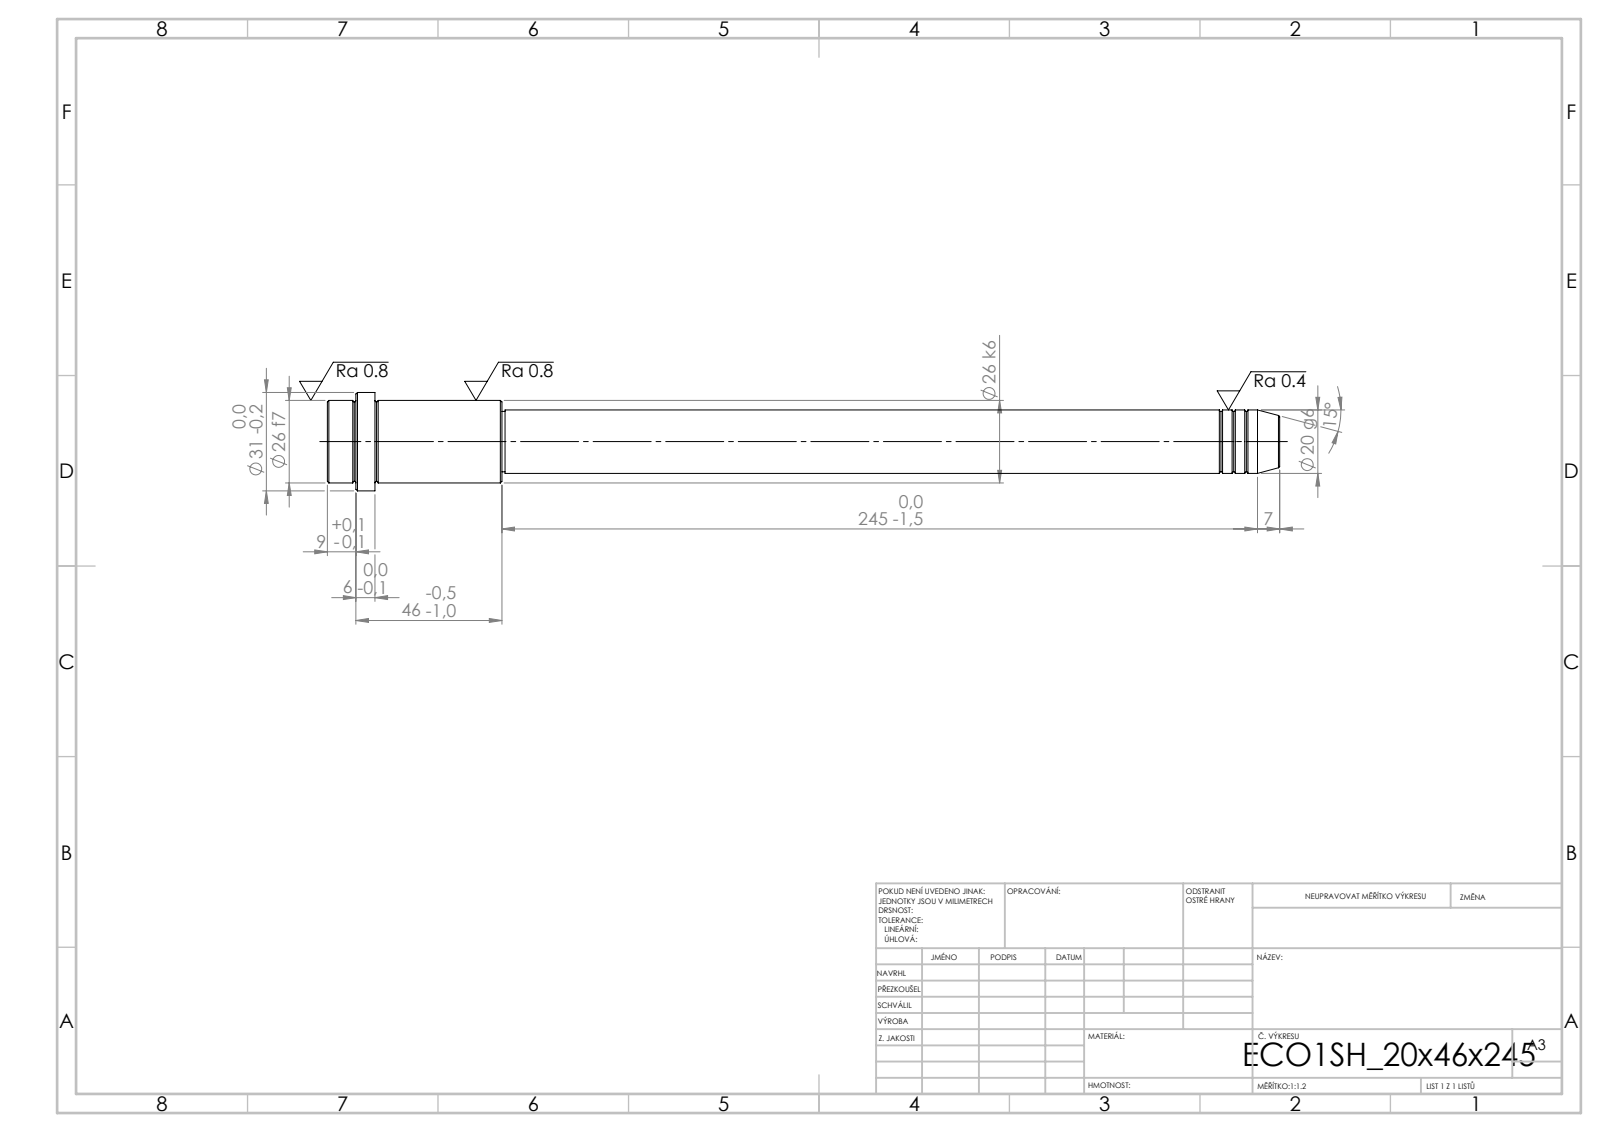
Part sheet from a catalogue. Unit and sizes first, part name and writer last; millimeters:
Units: millimetres
Overall size (bounding box): 300 × 31 × 31
Round bosses / shafts (diameter × count): ⌀31 ×1, ⌀26 ×1, ⌀20 ×1, ⌀19 ×1
Main face-to-face distances: 15, 40, 55, 245, 285, 300, 291, 46, 6, 9
Volume: 106 927 mm³ · Surface area: 21 516 mm²
Bodies: 1 solid, 52 faces (6 planar, 16 cylindrical, 30 other)
STEP written by: SolidWorks 2019 (CONFIG_CONTROL_DESIGN)
